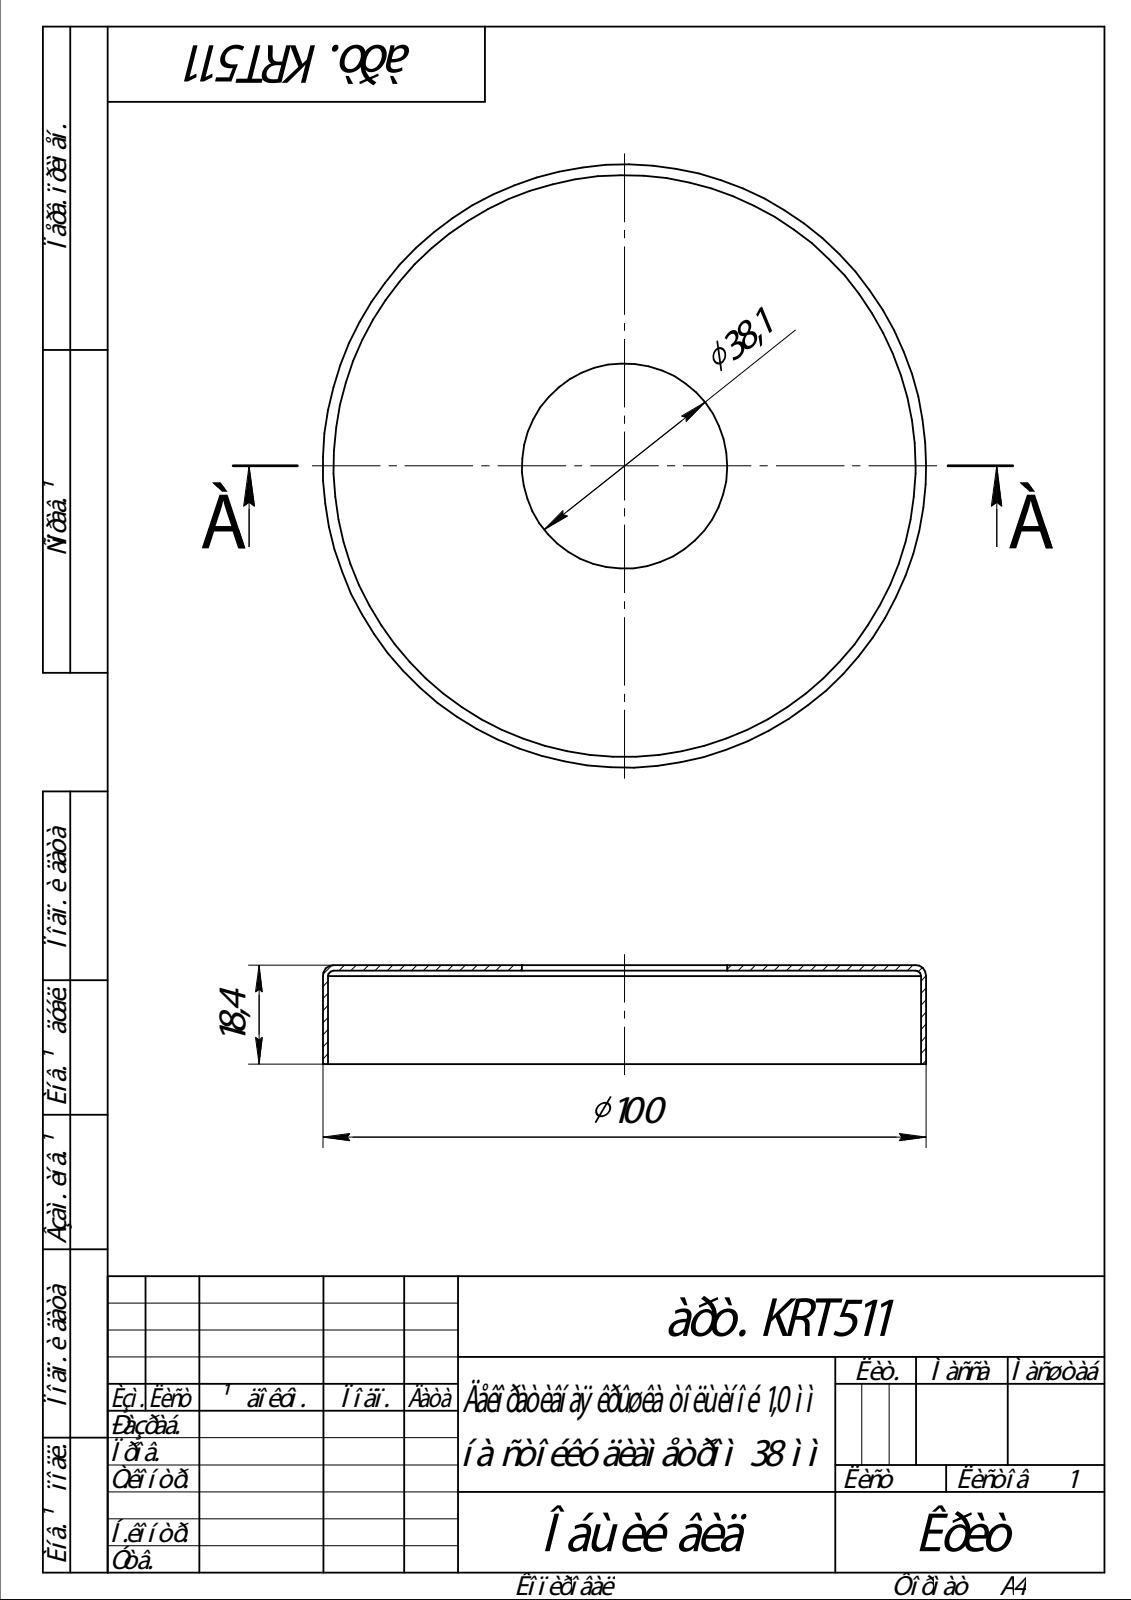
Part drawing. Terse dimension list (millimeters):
name: арт. KRT511
written by: SolidWorks 2014 (AUTOMOTIVE_DESIGN)
unit: mm
bodies: 1 solid, 13 faces (3 planar, 6 cylindrical, 4 other)
size: 112 × 112 × 18.4
volume: 14 554 mm³; area: 29 578 mm²
holes: 1× ⌀38.1, 1× ⌀110
bosses: 1× ⌀112
face distances: 1, 17.4, 18.4
